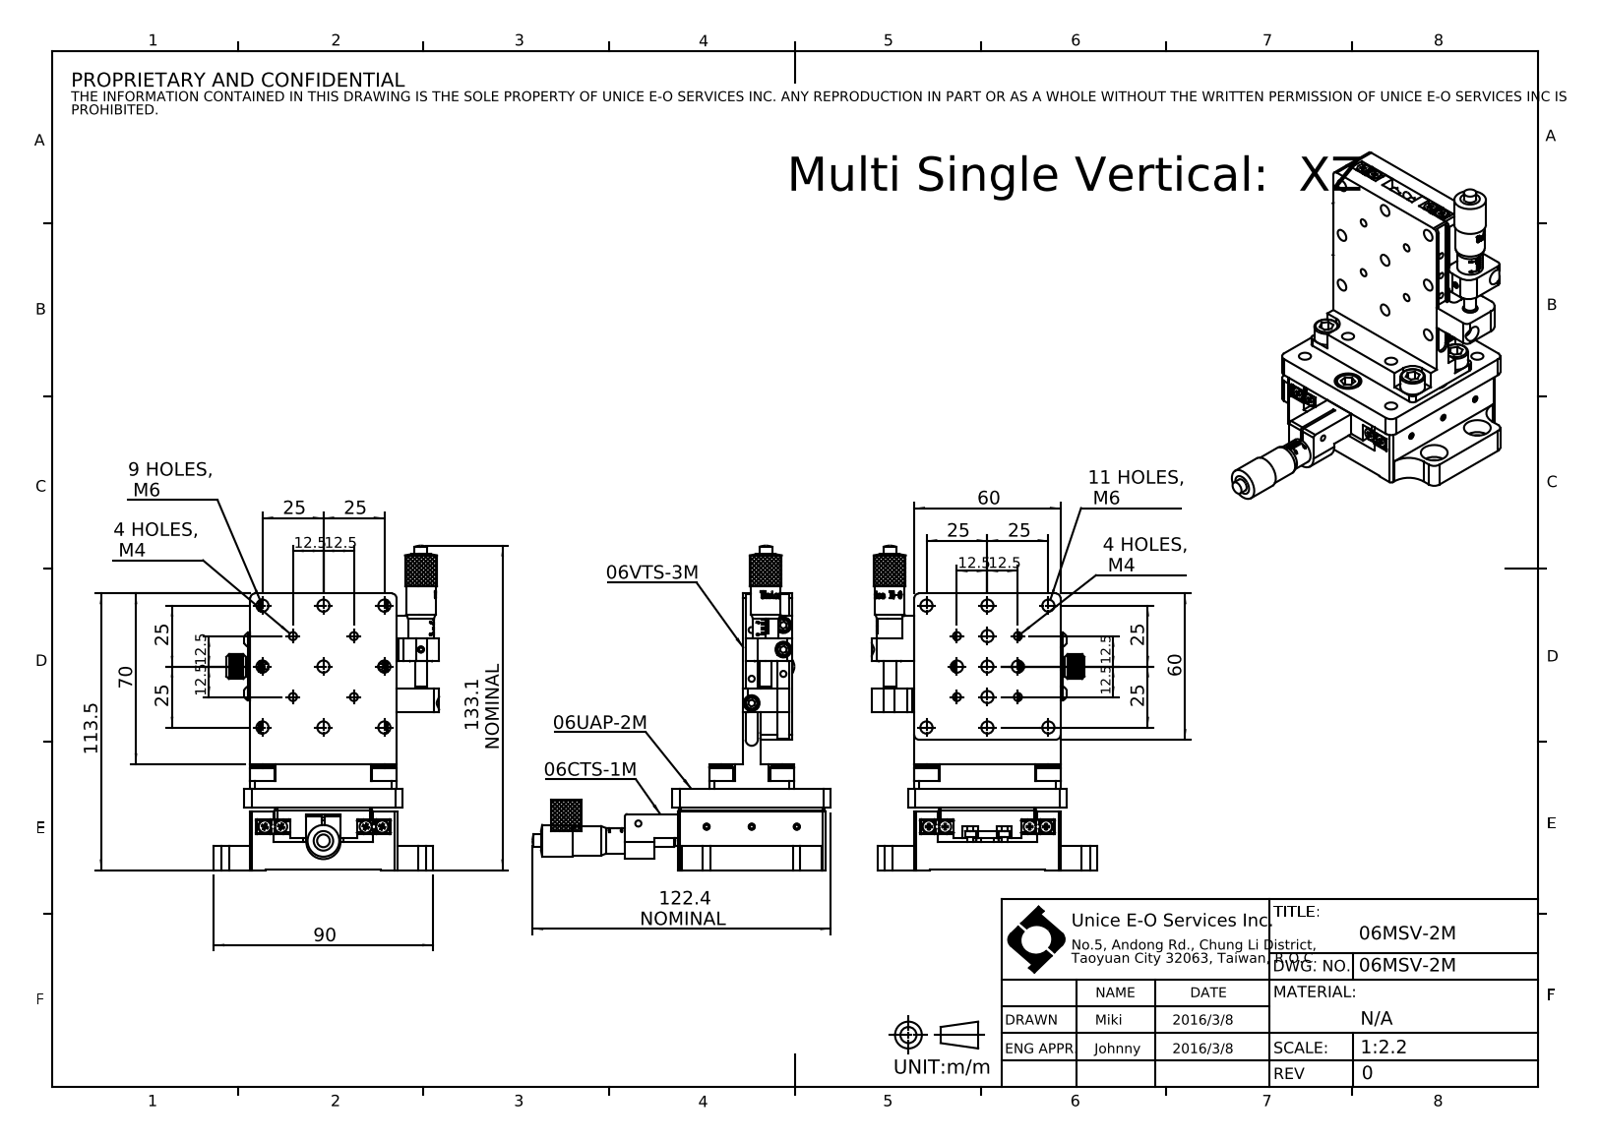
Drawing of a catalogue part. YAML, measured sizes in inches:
part_name: "06MSV-2M"
step_written_by: "SolidWorks 2016 (CONFIG_CONTROL_DESIGN)"
units: inches
bodies: {solids: 93, faces: 3041, planar: 1628, cylindrical: 775, other: 638}
overall_size: [5.242, 4.819, 3.642]
volume: 13.4
surface_area: 172.5
round_holes:
  - {diameter: 0.197, count: 50}
  - {diameter: 0.081, count: 34}
  - {diameter: 0.098, count: 23}
  - {diameter: 0.118, count: 19}
  - {diameter: 0.26, count: 9}
  - {diameter: 0.433, count: 9}
  - {diameter: 0.13, count: 8}
  - {diameter: 0.315, count: 5}
  - {diameter: 0.134, count: 4}
  - {diameter: 0.177, count: 4}
  - {diameter: 0.256, count: 4}
  - {diameter: 0.276, count: 4}
round_bosses_or_shafts:
  - {diameter: 0.177, count: 26}
  - {diameter: 0.098, count: 26}
  - {diameter: 0.118, count: 17}
  - {diameter: 0.236, count: 9}
  - {diameter: 0.394, count: 8}
  - {diameter: 0.197, count: 8}
  - {diameter: 0.1, count: 8}
  - {diameter: 0.217, count: 5}
partial_cylinders:
  - {radius: 0.039, count: 13}
  - {radius: 0.079, count: 12}
  - {radius: 0.118, count: 8}
  - {radius: 0.122, count: 4}
  - {radius: 0.197, count: 4}
  - {radius: 0.217, count: 4}
  - {radius: 0.335, count: 4}
  - {radius: 0.069, count: 2}
face_to_face_distances: [0.236, 0.315, 0.276, 0.512, 0.551, 0.807, 0.787, 0.5, 0.992, 1.319]
hole_center_spacings: [0.984, 1.556, 0.696, 1.392, 0.787, 0.492, 1.1, 2.201]
